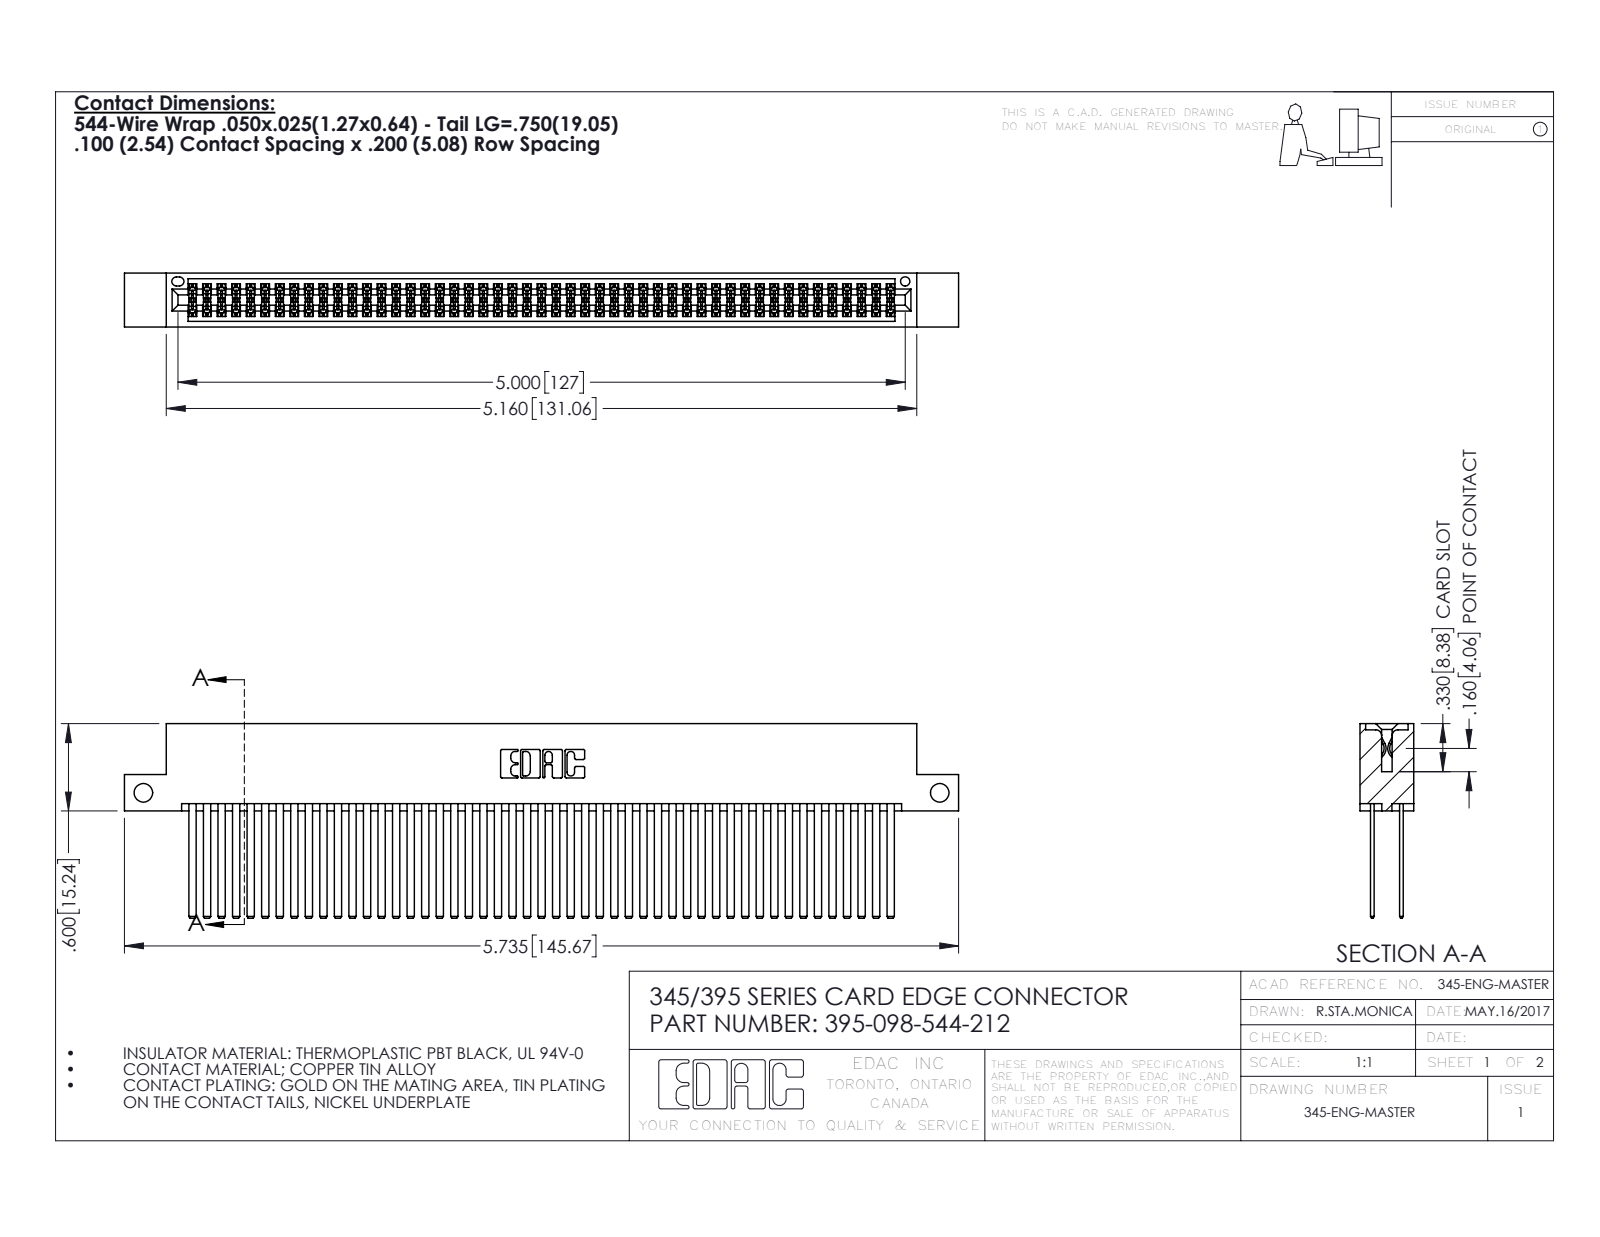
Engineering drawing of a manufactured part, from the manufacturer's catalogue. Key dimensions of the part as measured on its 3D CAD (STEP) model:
Part name (STEP PRODUCT): 395-098-544-212; 345-292-001_345-293-144; 345 Part_Flush Mounting Lugs - Side Mount
STEP written by: SolidWorks 2016 (CONFIG_CONTROL_DESIGN)
Units: inches
Bodies: 99 solids, 4438 faces (2922 planar, 1516 cylindrical, 0 other)
Overall size (bounding box): 5.735 × 1.337 × 0.37
Volume: 0.946 in³ · Surface area: 41.76 in²
Round holes (diameter × count): ⌀0.128 ×2, ⌀0.064 ×1
Partial cylindrical surfaces — rounded edges, fillets, slot ends (radius × count): R0.006 ×147, R0.01 ×22, R0.007 ×6, R0.031 ×6, R0.026 ×3, R0.014 ×2, R0.019 ×2, R0.022 ×2
Main face-to-face distances: 0.2, 0.025, 0.298, 0.072, 0.098, 0.272, 0.225, 0.175, 0.37, 0.05
Hole centre spacings: 5.475
